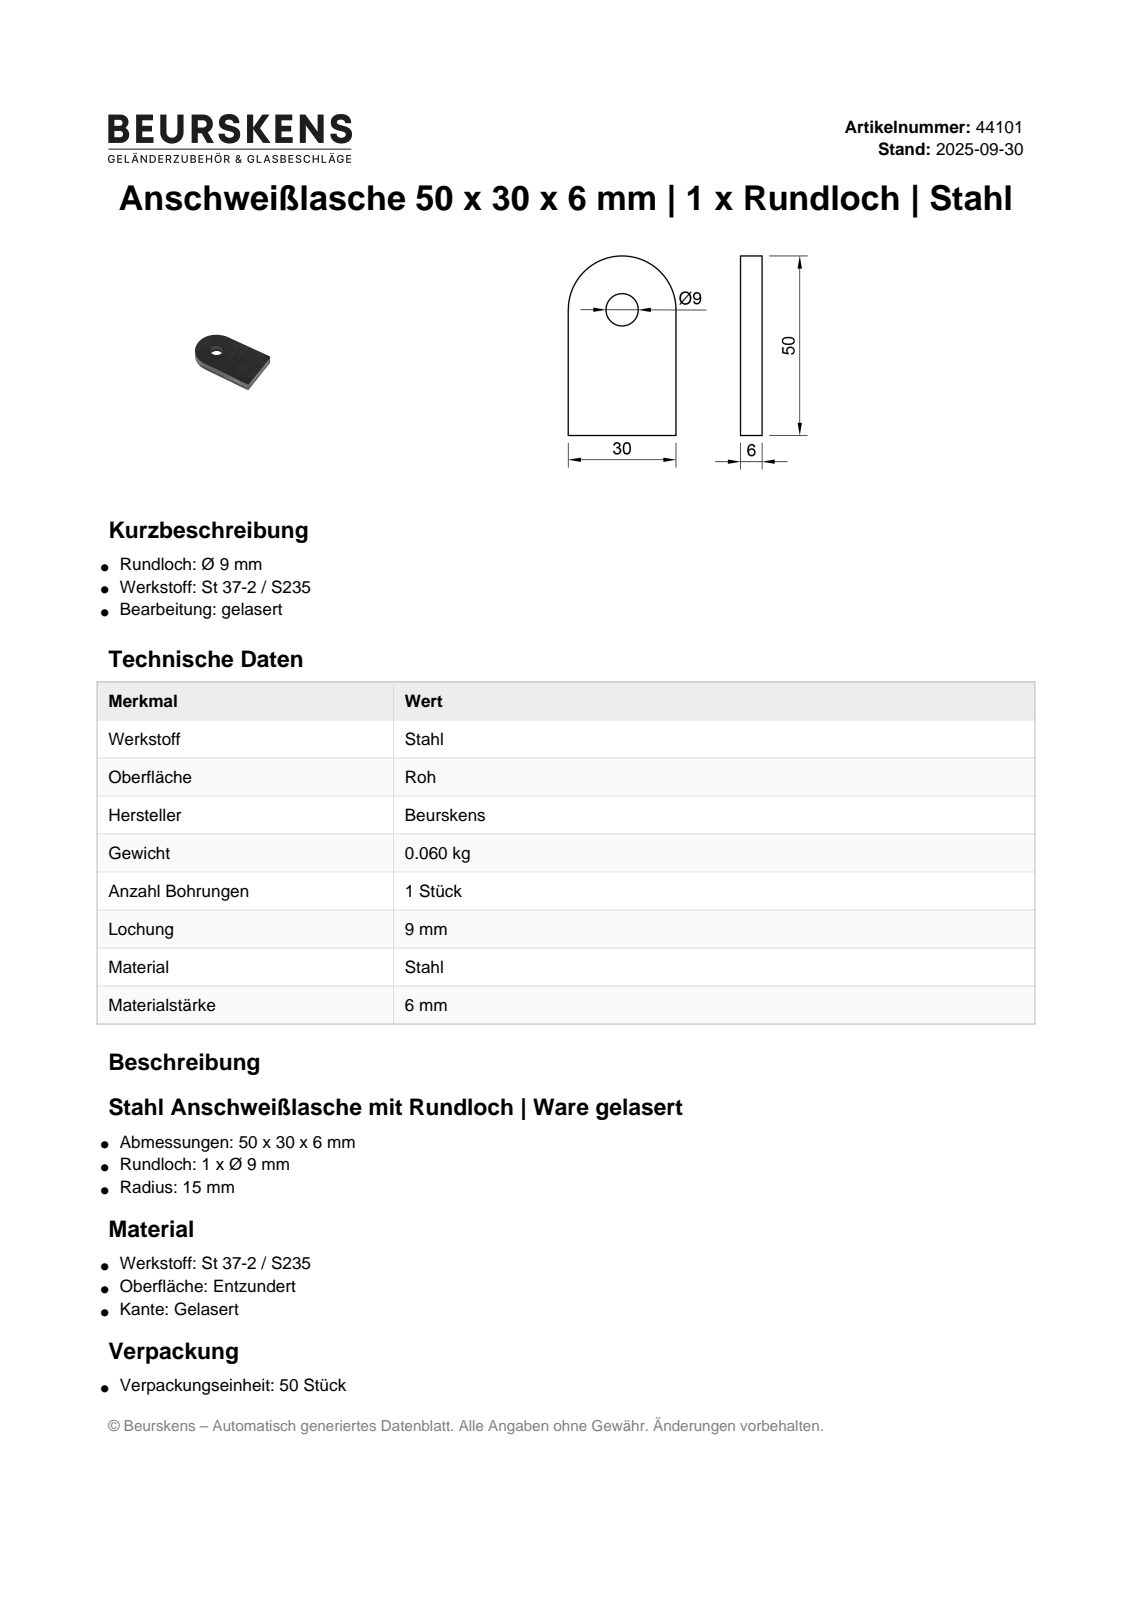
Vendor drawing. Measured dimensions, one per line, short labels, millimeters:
name: 44101
written by: Autodesk Inventor 2023 (AUTOMOTIVE_DESIGN)
unit: mm
bodies: 1 solid, 7 faces (5 planar, 2 cylindrical, 0 other)
size: 50 × 30 × 6
volume: 8 039 mm³; area: 3 732 mm²
holes: 1× ⌀9
rounds: 1× R15
face distances: 6, 30
